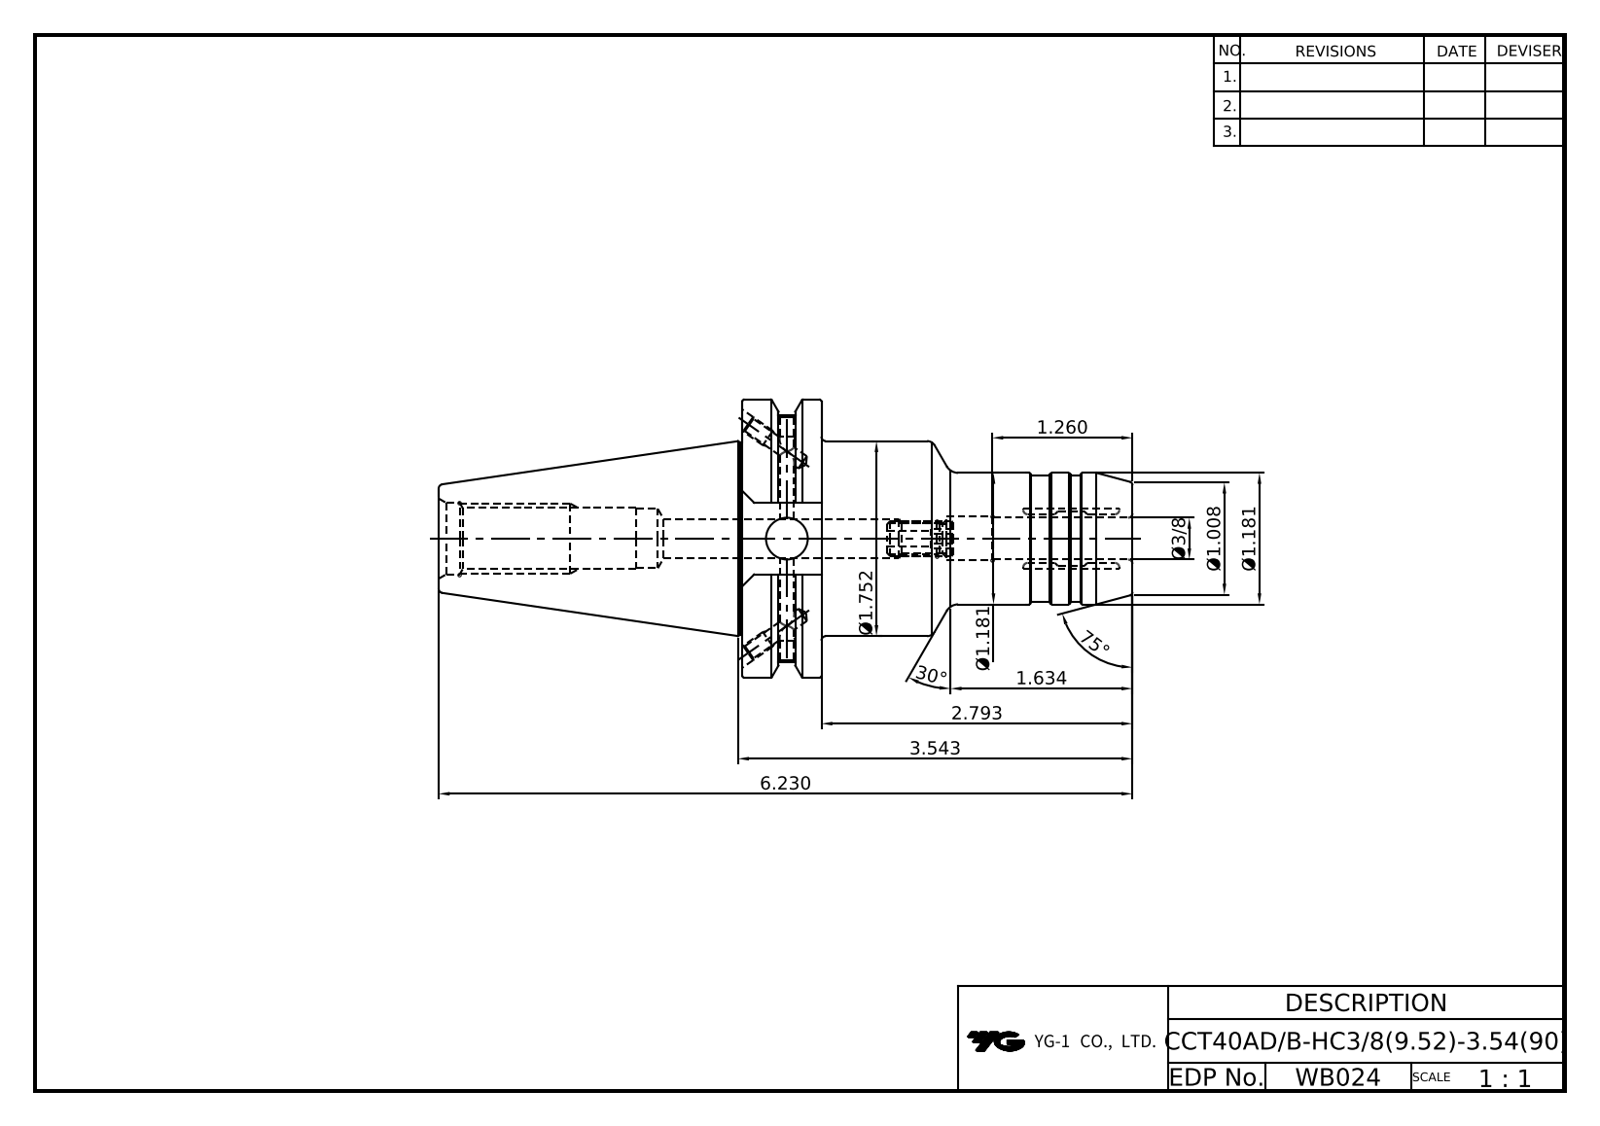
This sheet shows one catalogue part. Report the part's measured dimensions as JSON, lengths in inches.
{"part_name": "LO-CCT40ADB-HC9.525-90", "step_written_by": "Autodesk Inventor 2022 (AUTOMOTIVE_DESIGN)", "units": "inches", "bodies": {"solids": 1, "faces": 108, "planar": 34, "cylindrical": 35, "other": 39}, "overall_size": [6.23, 2.5, 2.405], "volume_in3": 10.61, "surface_area_in2": 46.41, "round_holes": [[0.128, 4], [0.157, 2], [0.165, 2], [0.375, 2], [0.272, 1], [0.354, 1], [0.394, 1], [0.512, 1], [0.527, 1], [0.642, 1]], "round_bosses_or_shafts": [[2.5, 1], [1.752, 1], [1.724, 1], [1.181, 1], [1.142, 1]], "partial_cylinders_radius": [[1.108, 1]], "face_to_face_distances": [0.711, 3.504, 2.793, 1.874, 0.645, 2.726, 3.437, 6.23, 3.202, 0.476]}
